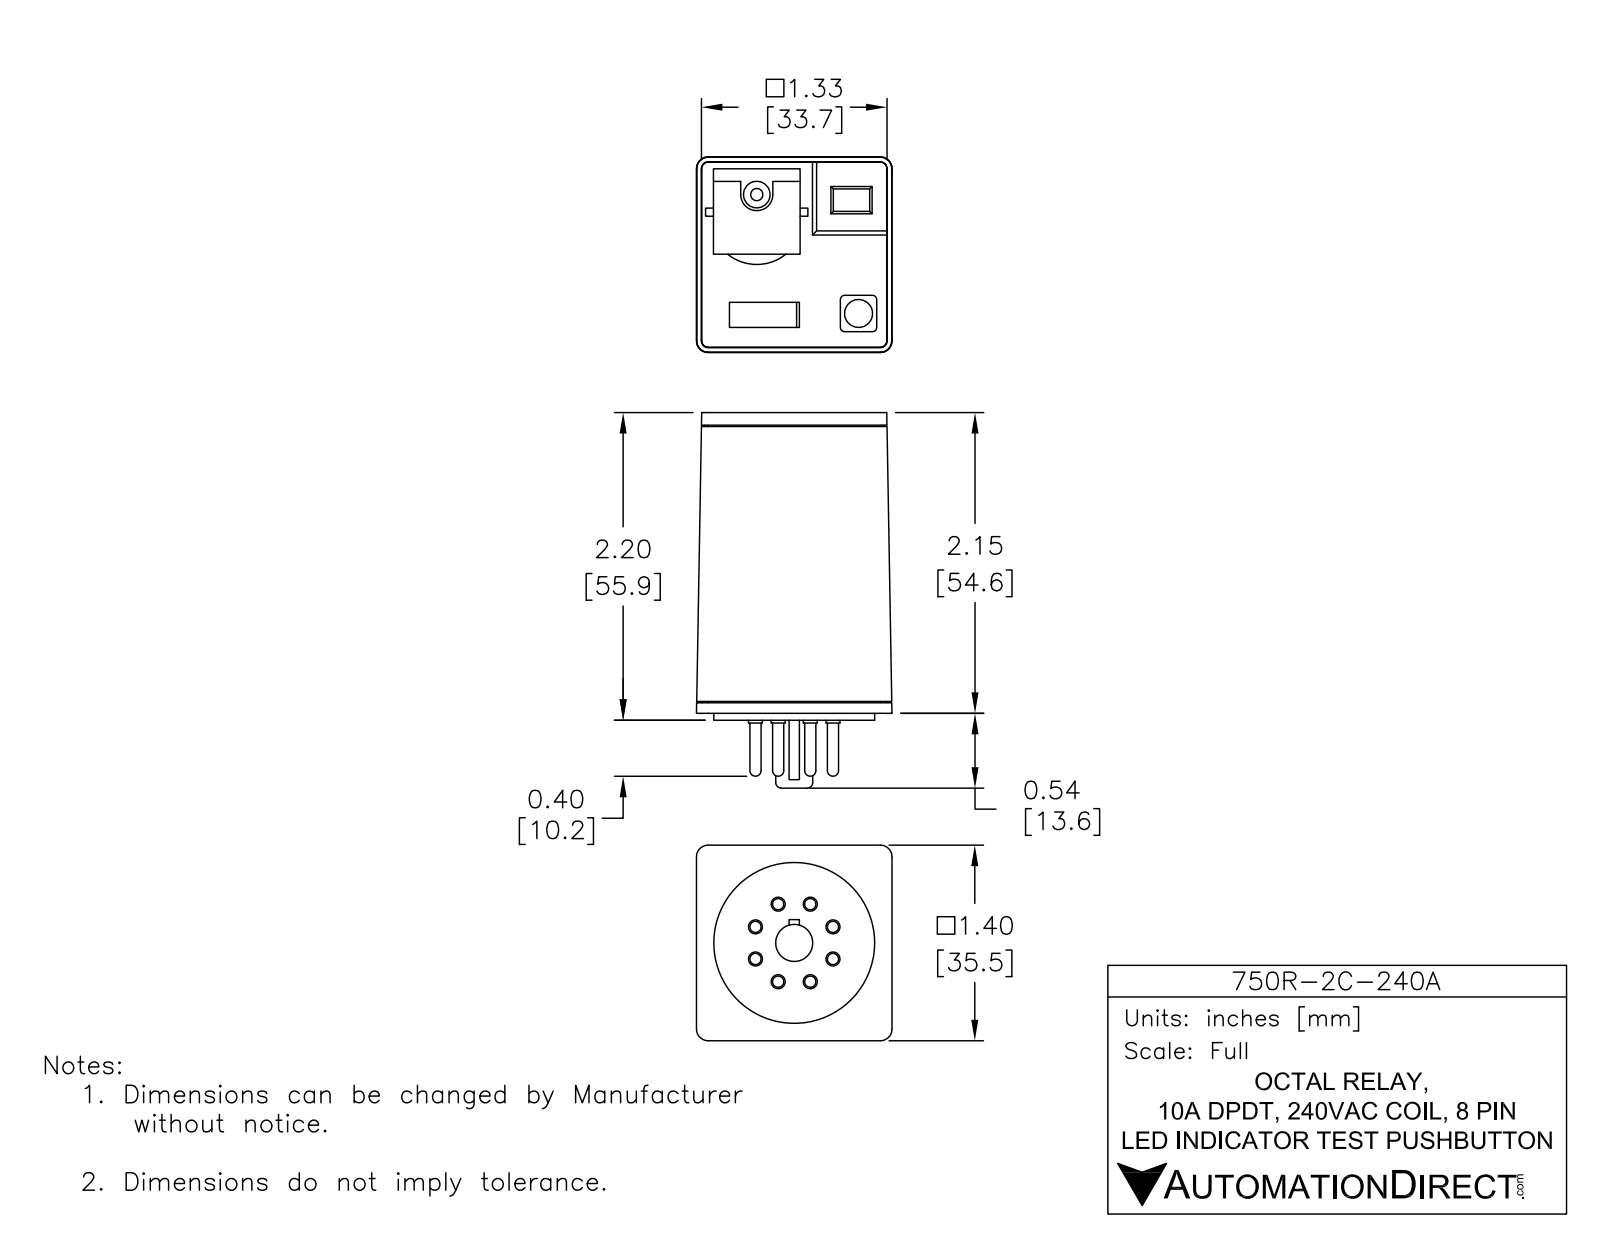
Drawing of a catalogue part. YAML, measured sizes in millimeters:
part_name: "750R-2C-240A"
step_written_by: "SolidWorks 2014 (AUTOMOTIVE_DESIGN)"
units: millimeters
bodies: {solids: 1, faces: 162, planar: 90, cylindrical: 50, other: 22}
overall_size: [68.2, 35.5, 35.5]
volume: 66320
surface_area: 11210
round_holes:
  - {diameter: 2.2, count: 1}
  - {diameter: 5.1, count: 1}
round_bosses_or_shafts:
  - {diameter: 2.5, count: 8}
  - {diameter: 2, count: 8}
  - {diameter: 29.2, count: 1}
  - {diameter: 6.7, count: 1}
  - {diameter: 4.8, count: 1}
partial_cylinders:
  - {radius: 0.8, count: 4}
  - {radius: 2.9, count: 1}
  - {radius: 8.4, count: 1}
face_to_face_distances: [1.3, 54.6, 55.9, 53.6, 1, 55.6, 54.4, 2.2, 0.8, 54.9]
hole_center_spacings: [28.4]
